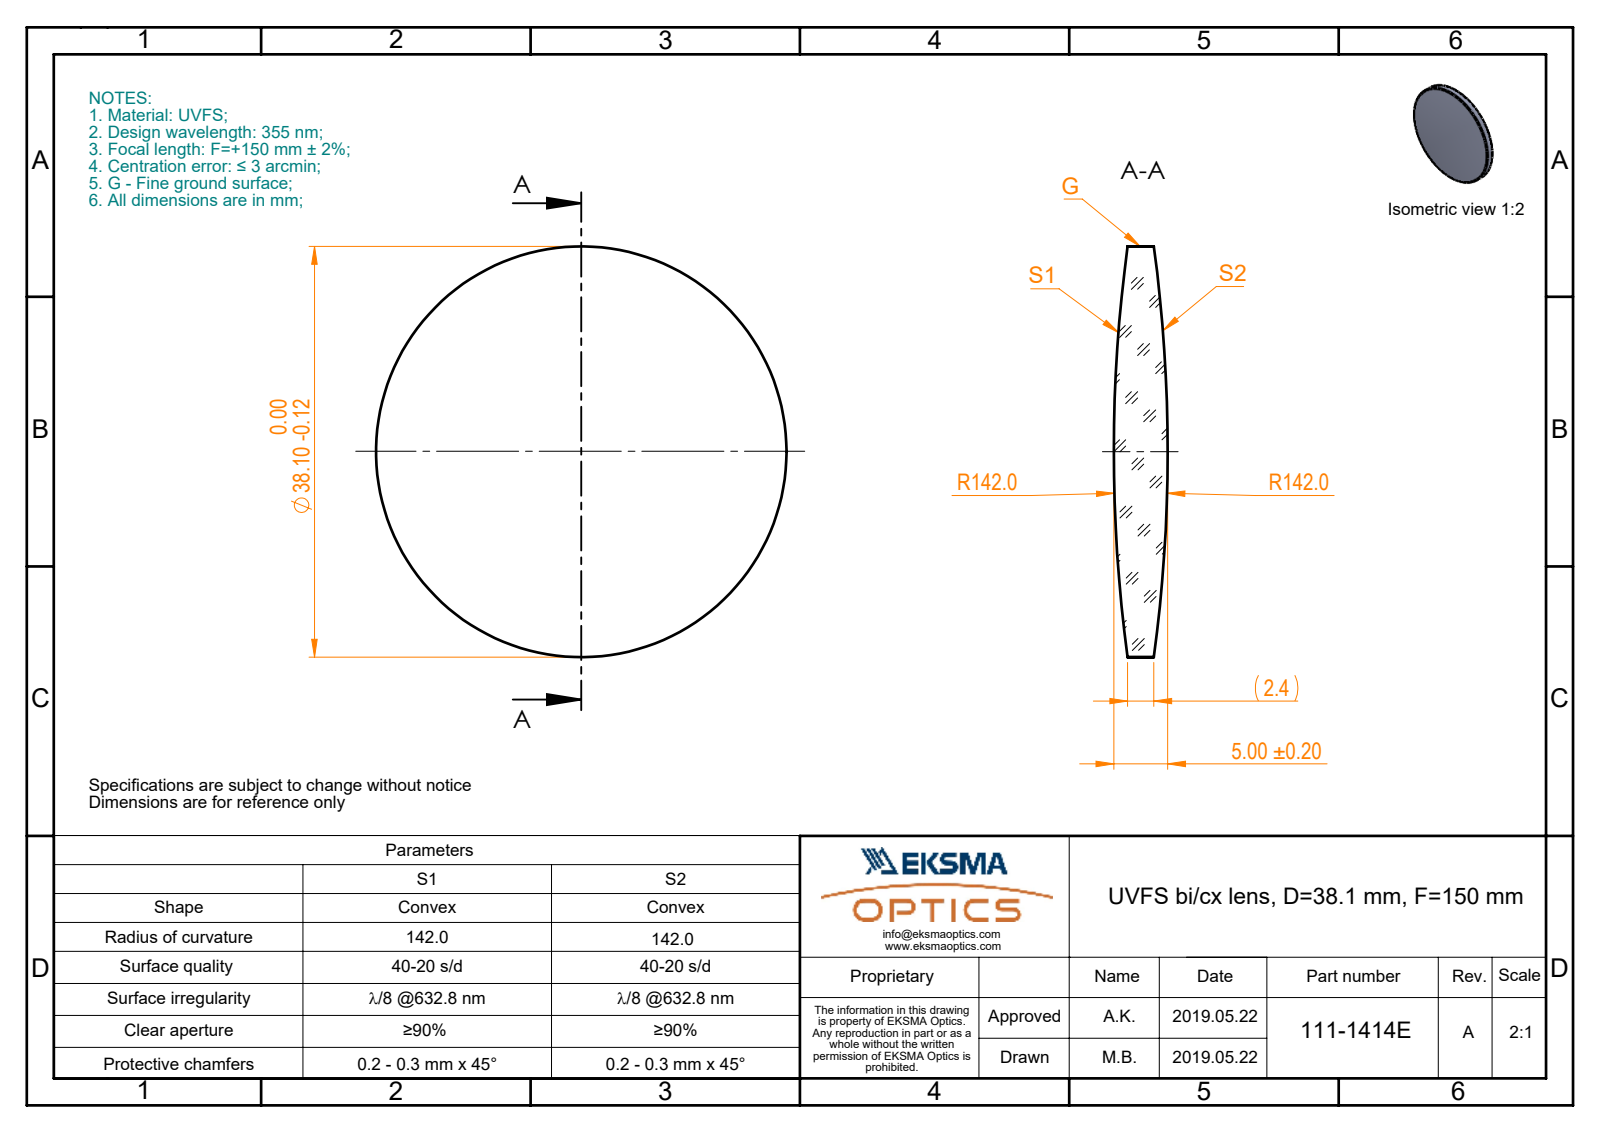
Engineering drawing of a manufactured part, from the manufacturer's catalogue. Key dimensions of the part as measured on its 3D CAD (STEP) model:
Part name (STEP PRODUCT): 111-1414E UVFS bi-cx 38.1 F150
STEP written by: SolidWorks 2017 (CONFIG_CONTROL_DESIGN)
Units: millimetres
Bodies: 1 solid, 6 faces (0 planar, 2 cylindrical, 4 other)
Overall size (bounding box): 38.1 × 38.1 × 5
Volume: 4 239 mm³ · Surface area: 2 582 mm²
Round bosses / shafts (diameter × count): ⌀38.1 ×1
